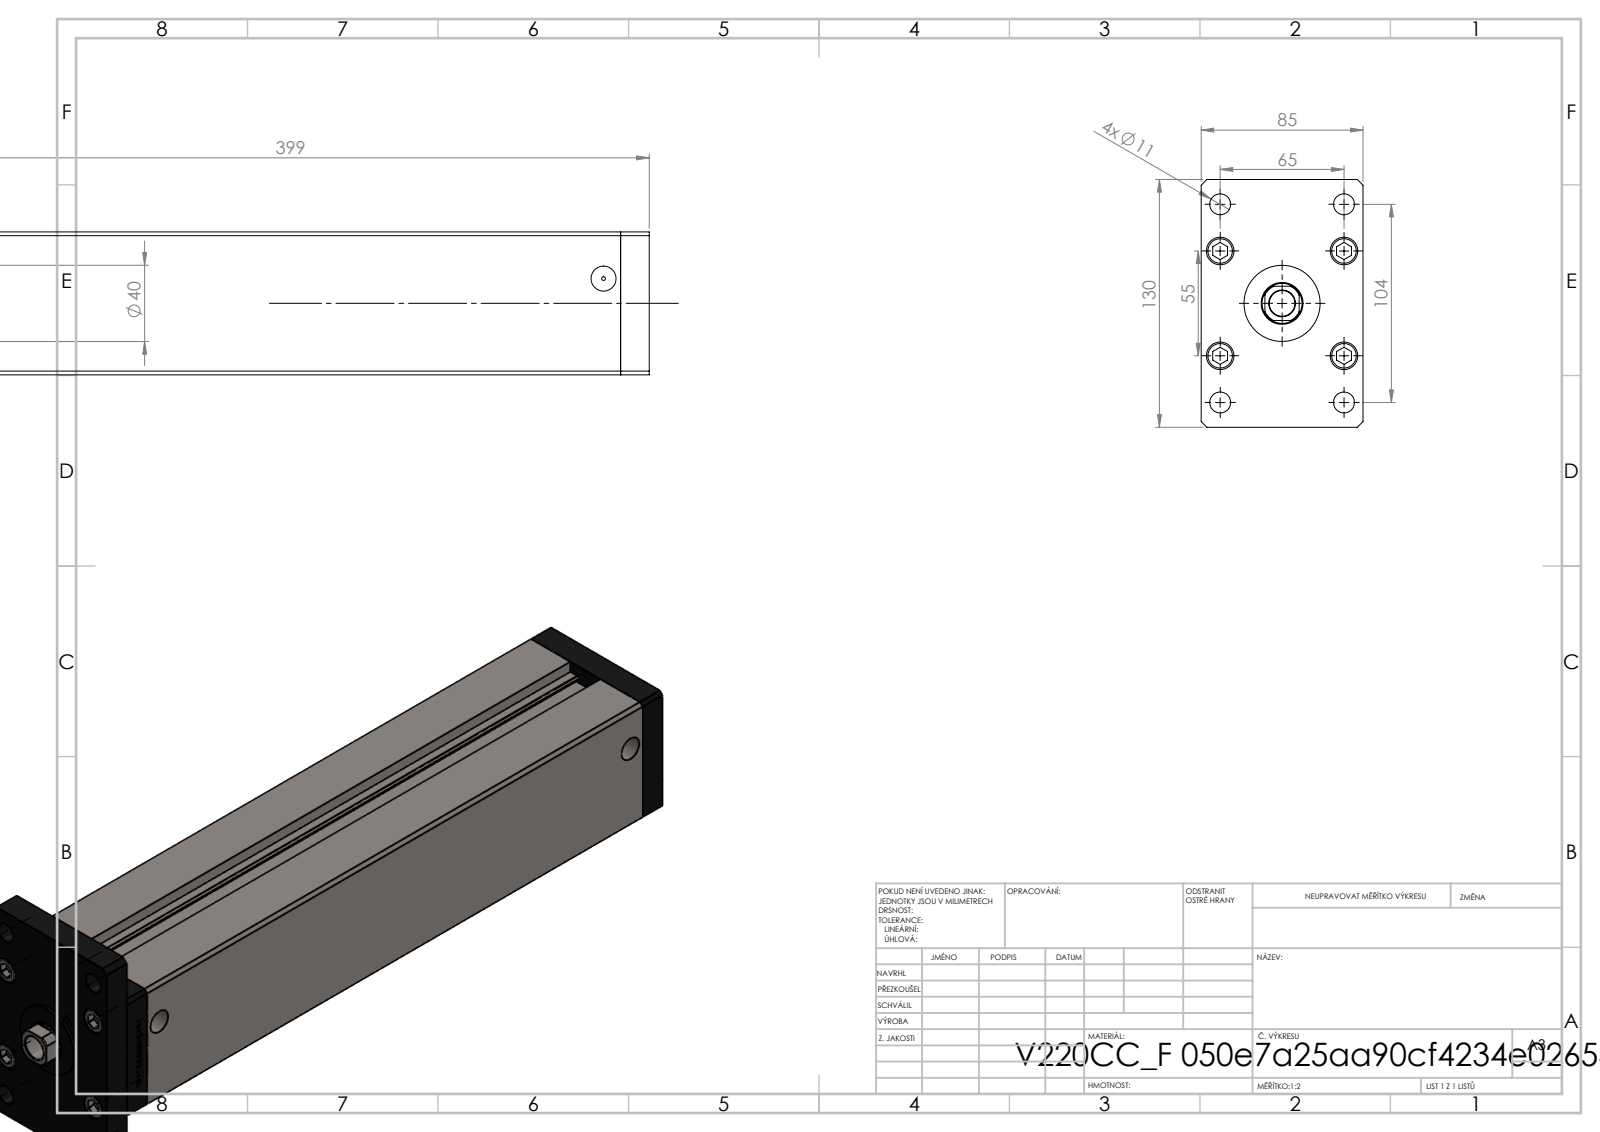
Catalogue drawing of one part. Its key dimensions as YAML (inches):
part_name: "V220C_F; V220C_VC_F; V220C BACK_F; V220C_FRONT_F (+2 more)"
step_written_by: "SolidWorks 2019 (CONFIG_CONTROL_DESIGN)"
units: inches
bodies: {solids: 19, faces: 1308, planar: 515, cylindrical: 187, other: 606}
overall_size: [16.732, 5.118, 3.346]
volume: 142.2
surface_area: 490.4
round_holes:
  - {diameter: 0.433, count: 9}
  - {diameter: 0.61, count: 5}
  - {diameter: 0.394, count: 4}
  - {diameter: 0.571, count: 4}
  - {diameter: 0.079, count: 2}
  - {diameter: 0.518, count: 2}
  - {diameter: 0.531, count: 1}
  - {diameter: 0.866, count: 1}
  - {diameter: 0.925, count: 1}
round_bosses_or_shafts:
  - {diameter: 0.315, count: 9}
  - {diameter: 0.571, count: 5}
  - {diameter: 1.575, count: 1}
partial_cylinders:
  - {radius: 0.037, count: 2}
  - {radius: 0.413, count: 1}
face_to_face_distances: [3.346, 0.591, 2.953, 15.098, 15.689, 14.508, 1.181, 0.413, 16.28, 2.539]
hole_center_spacings: [1.102, 0.965, 1.676, 2.414, 2.559, 2.735, 3.13, 4.043]
